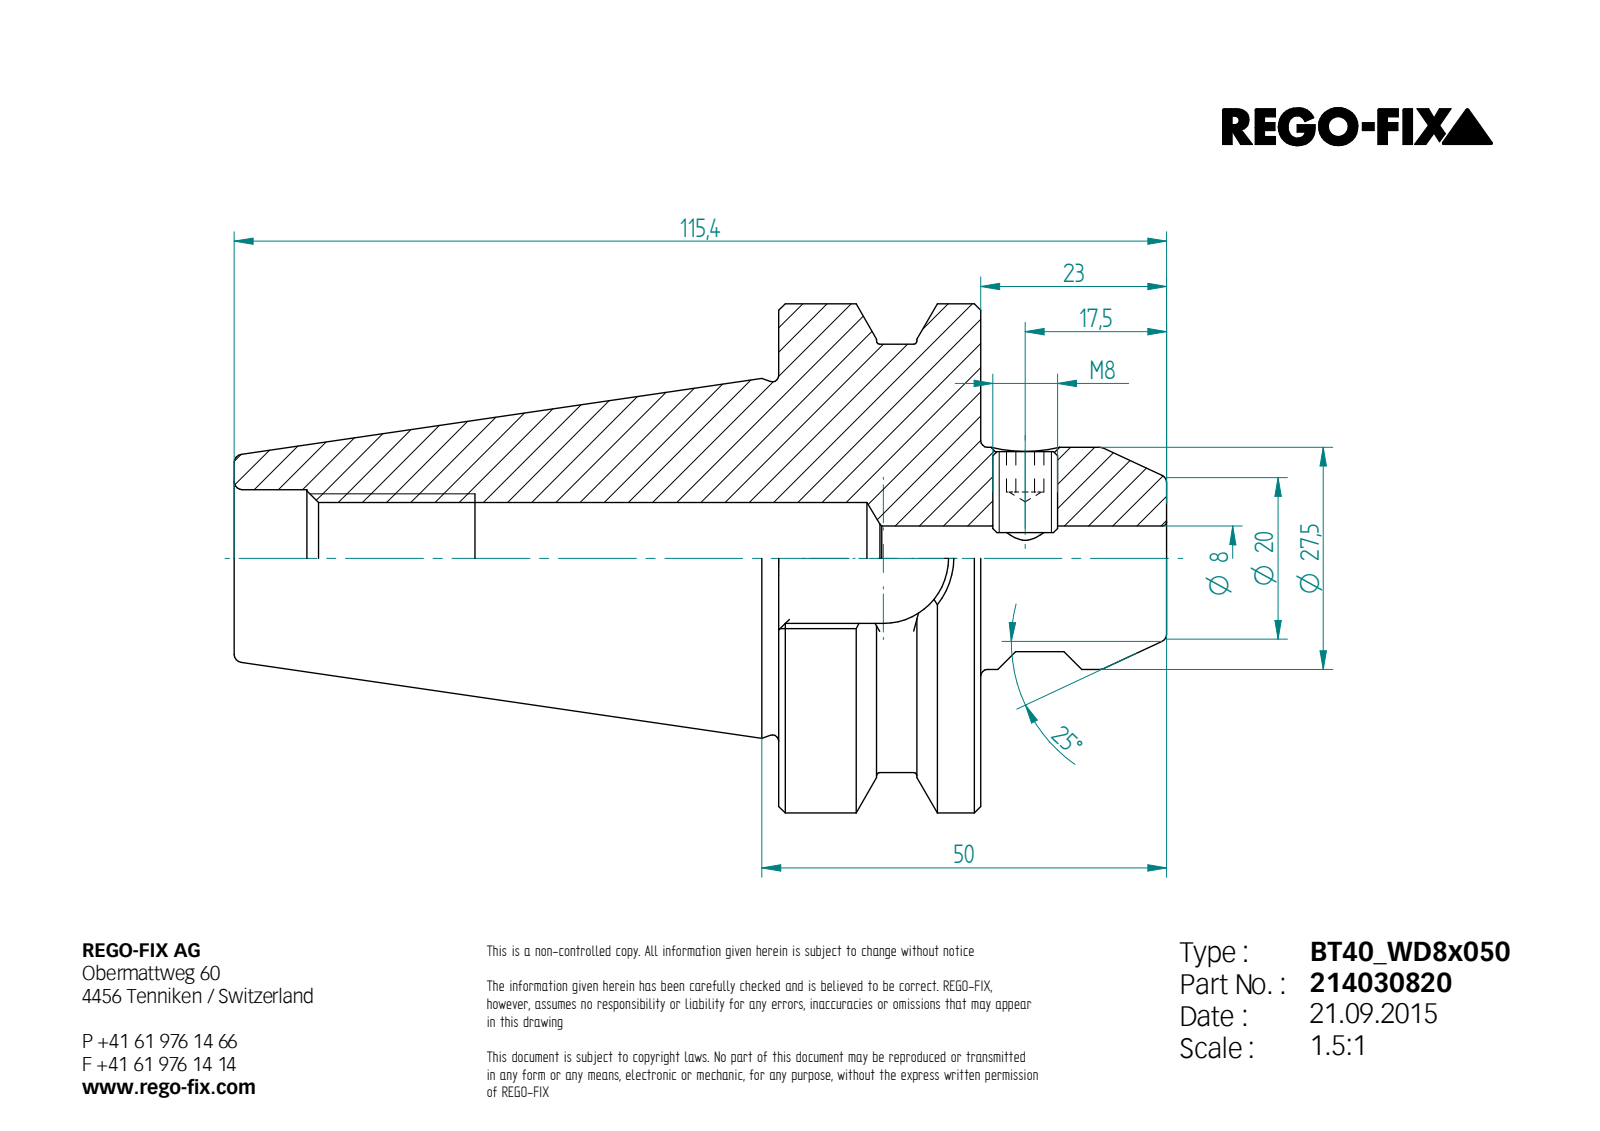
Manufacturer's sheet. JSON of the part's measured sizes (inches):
{"step_written_by": "Unknown (AUTOMOTIVE_DESIGN)", "units": "inches", "bodies": {"solids": 2, "faces": 103, "planar": 53, "cylindrical": 18, "other": 32}, "overall_size": [4.543, 2.48, 2.48], "volume_in3": 8.082, "surface_area_in2": 38.67, "round_holes": [[0.262, 1], [0.315, 1], [0.545, 1], [0.669, 1]], "round_bosses_or_shafts": [[2.48, 1], [2.087, 1], [1.083, 1], [0.315, 1]], "partial_cylinders_radius": [[0.02, 4], [0.317, 1]], "face_to_face_distances": [0.984, 1.776, 1.89, 0.906, 2.654, 3.638, 4.543, 0.634, 0.138, 0.772]}
